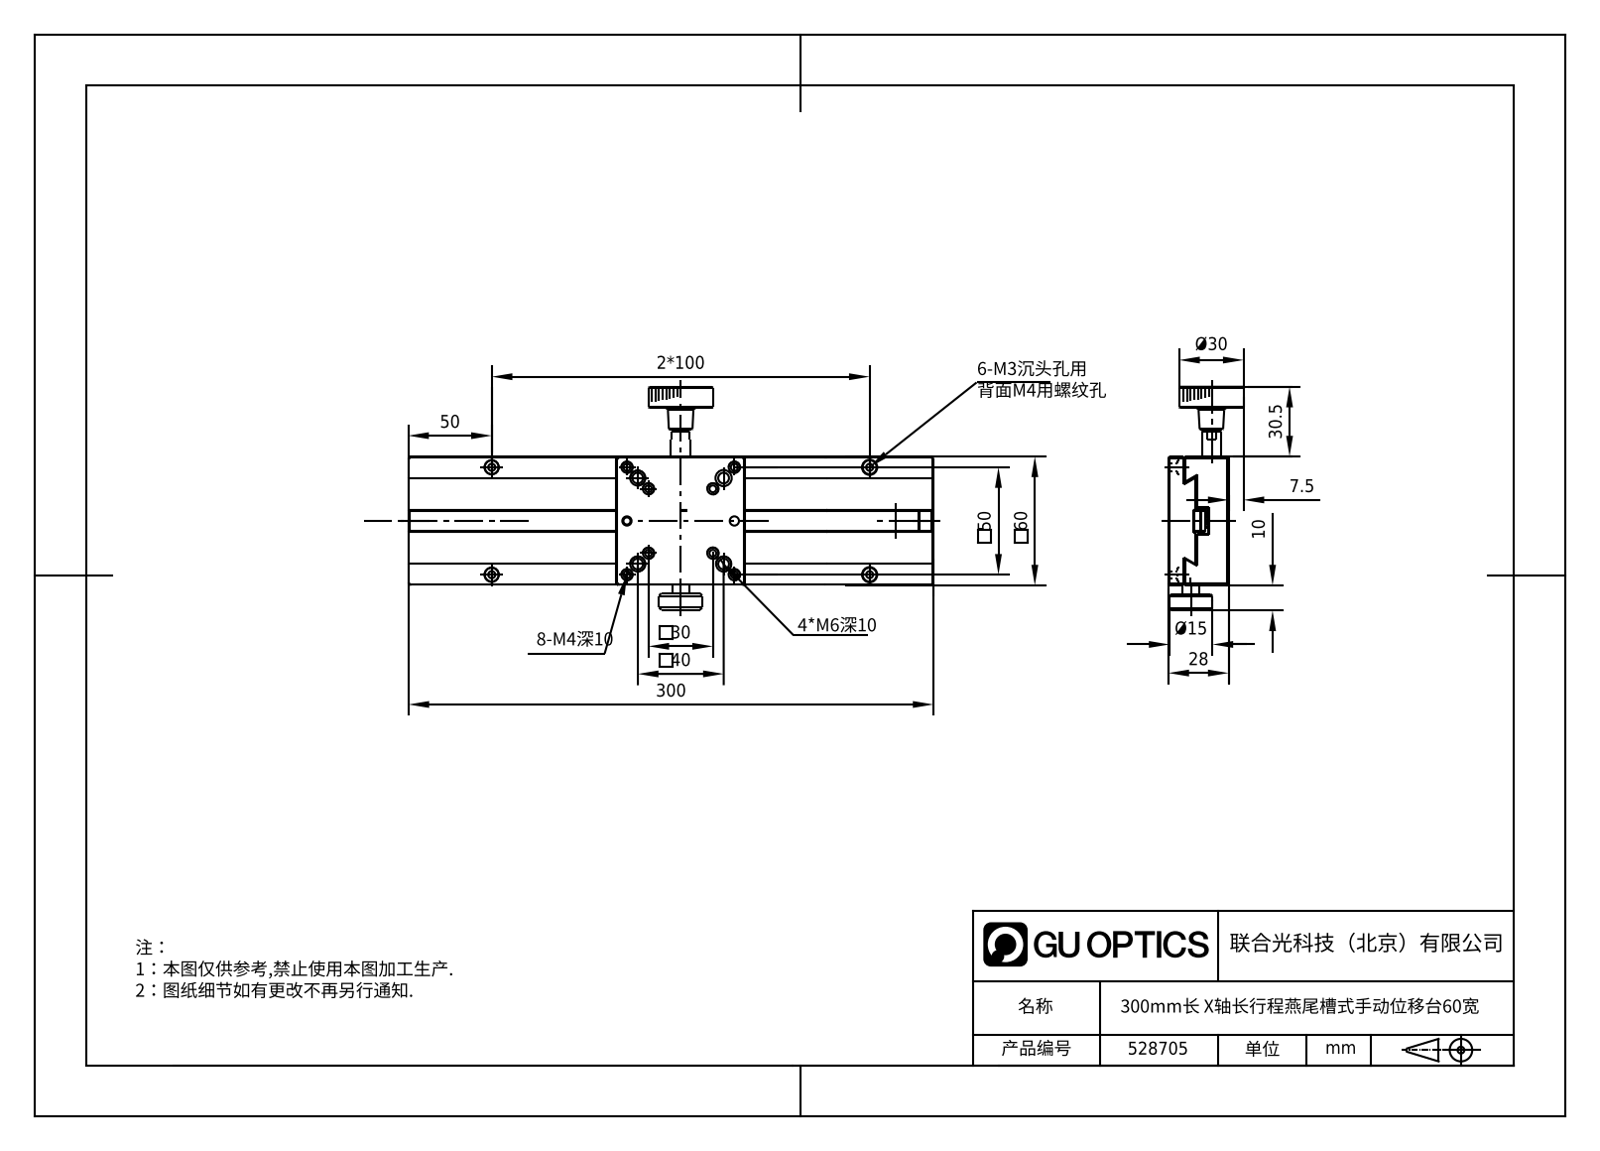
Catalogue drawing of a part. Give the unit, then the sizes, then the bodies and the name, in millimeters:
Units: millimetres
Overall size (bounding box): 300 × 101.79 × 32.73
Round holes (diameter × count): ⌀3.3 ×17, ⌀2.5 ×10, ⌀5 ×9, ⌀2.05 ×6, ⌀2.9 ×6, ⌀6 ×6, ⌀4 ×1, ⌀4.1 ×1, ⌀4.5 ×1, ⌀8 ×1, ⌀10 ×1
Round bosses / shafts (diameter × count): ⌀3 ×5, ⌀4.5 ×4, ⌀2.5 ×4, ⌀9 ×2, ⌀4 ×2, ⌀30 ×1, ⌀10 ×1, ⌀8 ×1
Partial cylindrical surfaces — rounded edges, fillets, slot ends (radius × count): R1.05 ×1
Main face-to-face distances: 7.5, 12.2, 4.7, 9.9, 2.4, 2.3, 60, 28, 20.5, 18.1
Hole centre spacings: 35.36, 7.07, 18.03, 20.62, 25, 41.23, 42.72, 45.28
Volume: 251 935 mm³ · Surface area: 80 502 mm²
Bodies: 19 solids, 649 faces (296 planar, 154 cylindrical, 199 other)
Part name (STEP PRODUCT): 528705
STEP written by: SolidWorks 2020 (CONFIG_CONTROL_DESIGN)
